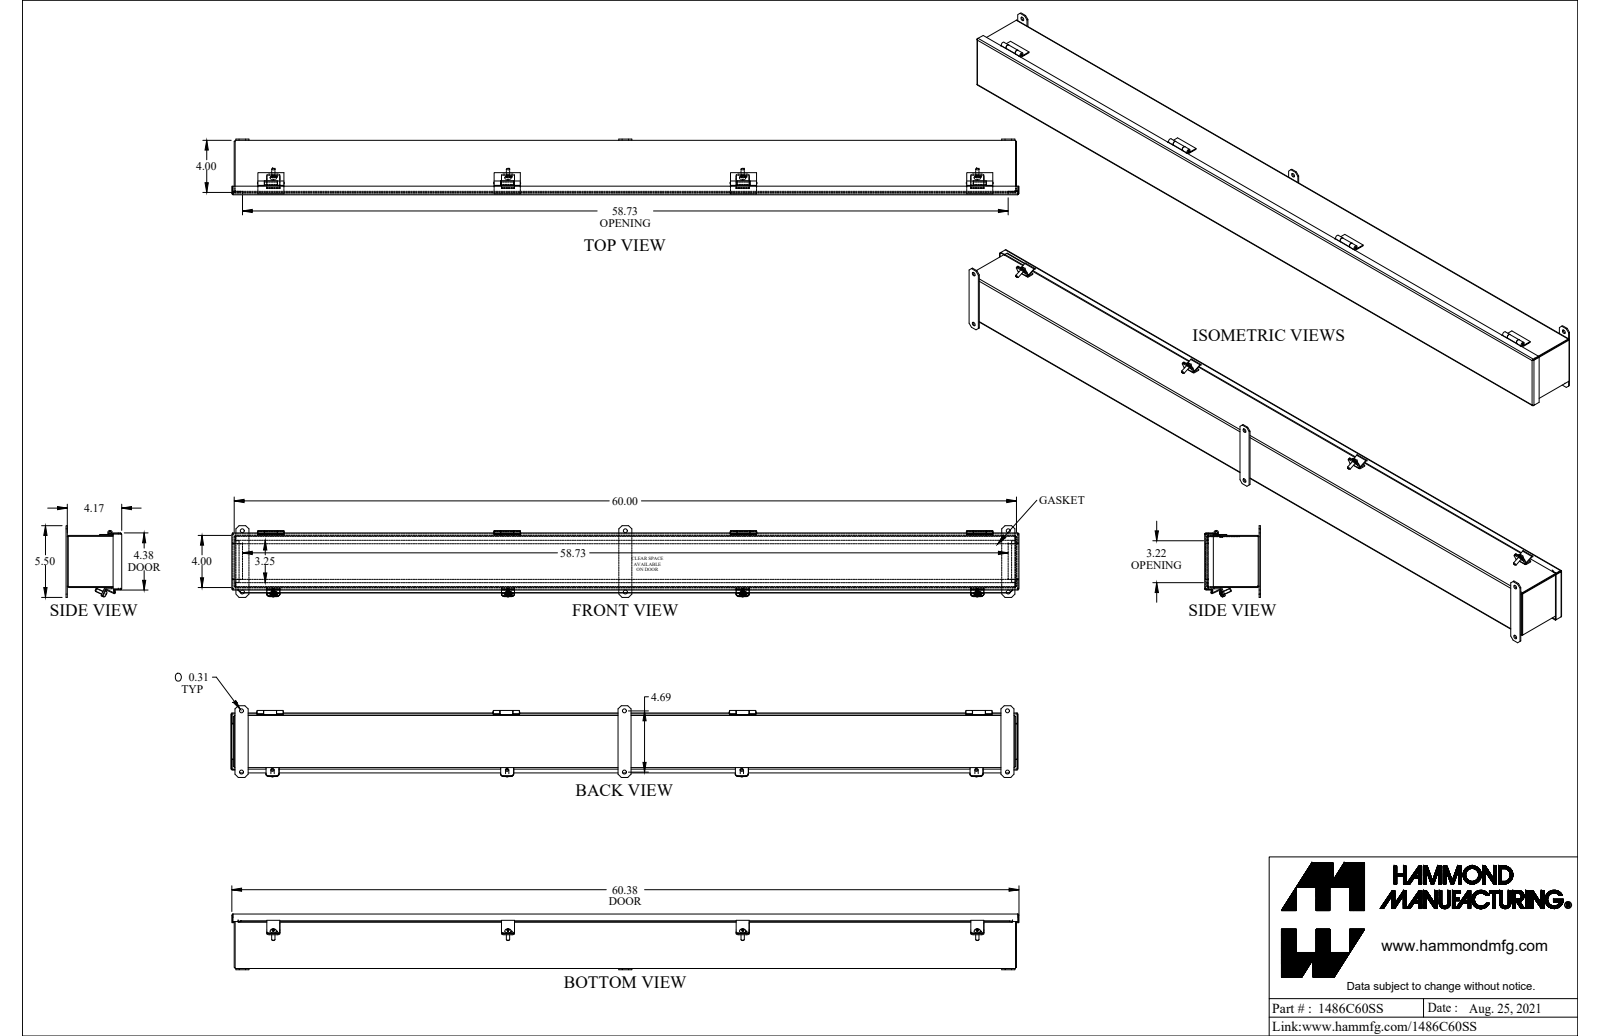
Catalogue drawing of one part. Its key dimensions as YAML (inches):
part_name: "1486C60SS"
step_written_by: "SolidWorks 2021 (AUTOMOTIVE_DESIGN)"
units: inches
bodies: {solids: 13, faces: 632, planar: 434, cylindrical: 160, other: 38}
overall_size: [60.375, 5.5, 4.267]
volume: 101.9
surface_area: 2546
round_holes:
  - {diameter: 0.313, count: 6}
  - {diameter: 0.213, count: 4}
  - {diameter: 0.187, count: 1}
round_bosses_or_shafts:
  - {diameter: 0.483, count: 4}
  - {diameter: 0.25, count: 4}
  - {diameter: 0.337, count: 1}
  - {diameter: 0.18, count: 1}
partial_cylinders:
  - {radius: 0.188, count: 16}
  - {radius: 0.036, count: 11}
  - {radius: 0.108, count: 11}
  - {radius: 0.01, count: 8}
  - {radius: 0.03, count: 8}
  - {radius: 0.141, count: 8}
  - {radius: 0.029, count: 2}
  - {radius: 0.086, count: 2}
face_to_face_distances: [0.072, 3.928, 4.1, 3.856, 4, 4.028, 4.172, 0.187, 0.259, 3.913]
hole_center_spacings: [4.688, 18, 29.375, 29.746, 36, 29.375, 29.747, 54]
